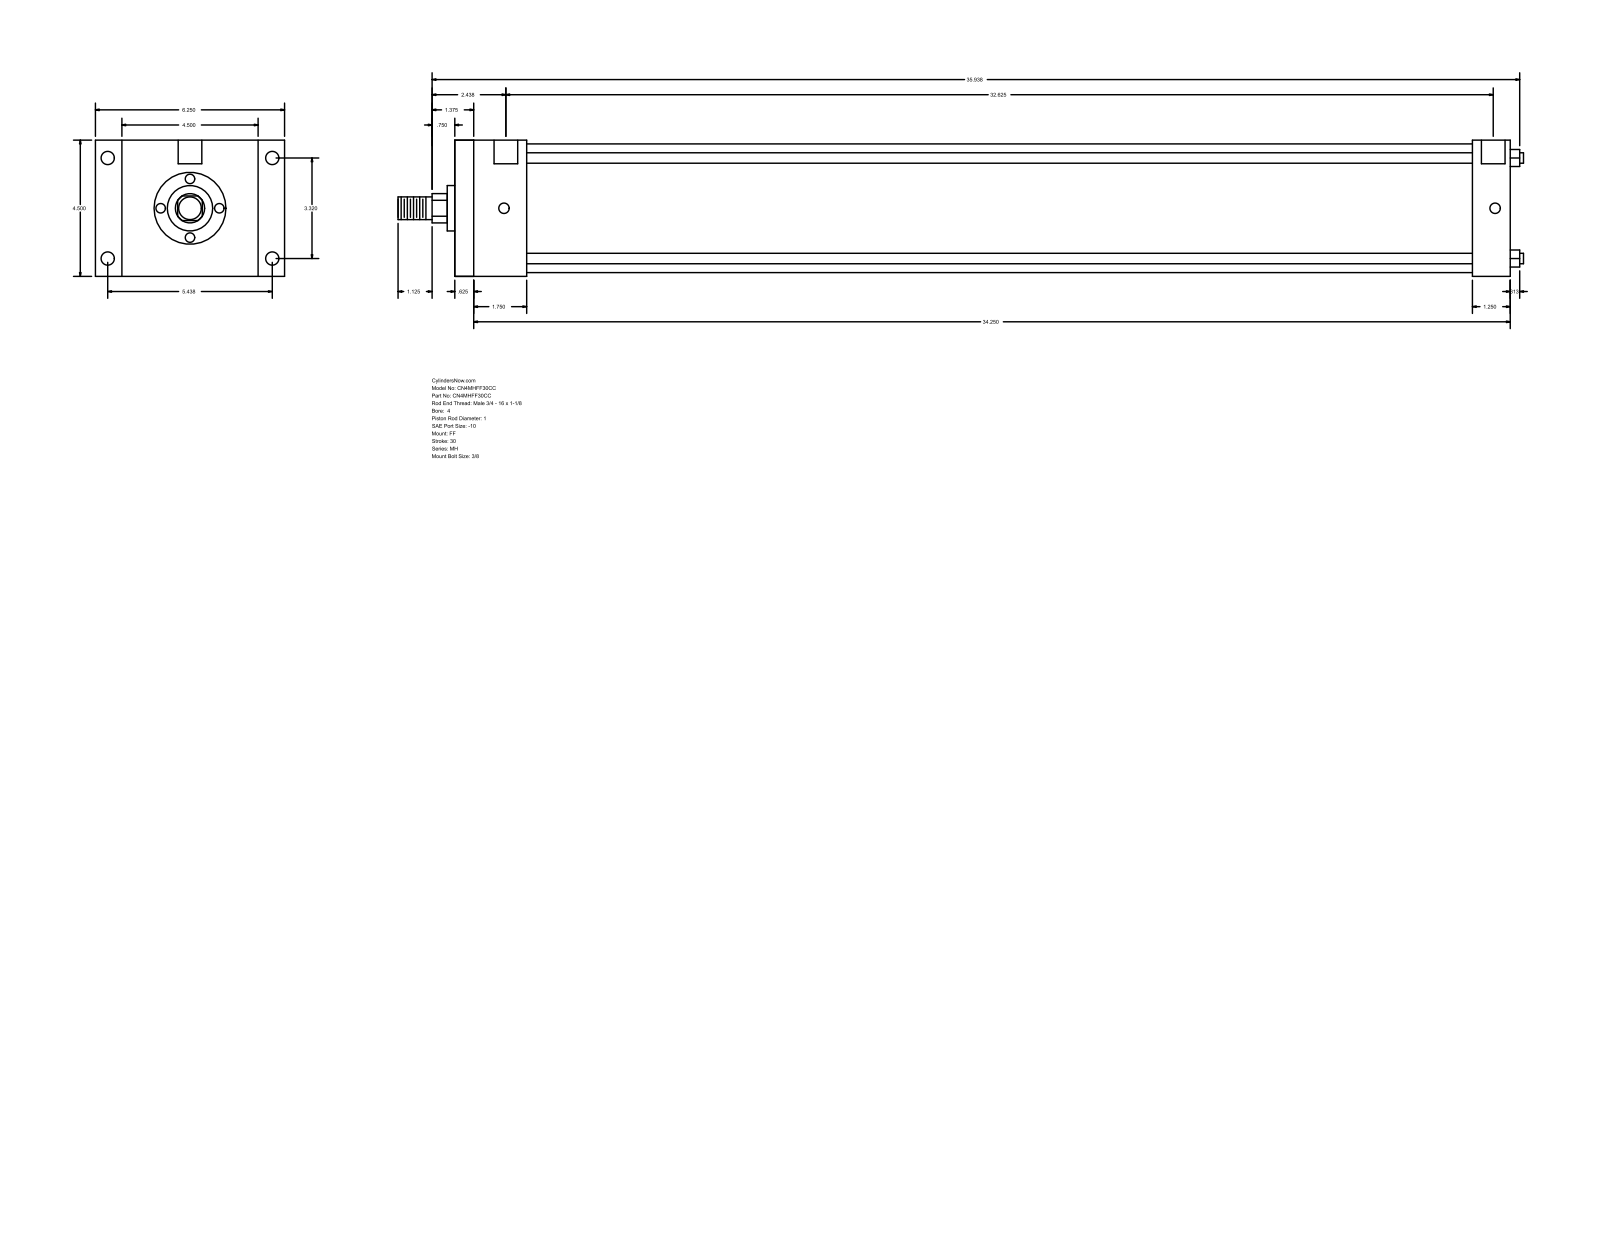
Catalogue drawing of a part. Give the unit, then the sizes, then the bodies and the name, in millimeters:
Units: millimetres
Overall size (bounding box): 944.56 × 158.75 × 114.3
Round holes (diameter × count): ⌀8.73 ×4, ⌀11.13 ×4, ⌀19.84 ×2
Round bosses / shafts (diameter × count): ⌀8.76 ×4, ⌀107.95 ×1, ⌀38.1 ×1, ⌀25.4 ×1, ⌀19.05 ×1
Partial cylindrical surfaces — rounded edges, fillets, slot ends (radius × count): R12.29 ×1
Main face-to-face distances: 114.3, 885.83, 15.87, 869.96, 60.33, 44.46, 825.5, 854.07, 838.2, 793.74
Hole centre spacings: 1.58, 84.32, 138.12, 161.82, 830.26, 831.84, 828.68
Bodies: 0 solids, 92 faces (64 planar, 28 cylindrical, 0 other)
Part name (STEP PRODUCT): MH_FF__0400_1
STEP written by: GSSL Pune (CONFIG_CONTROL_DESIGN)
